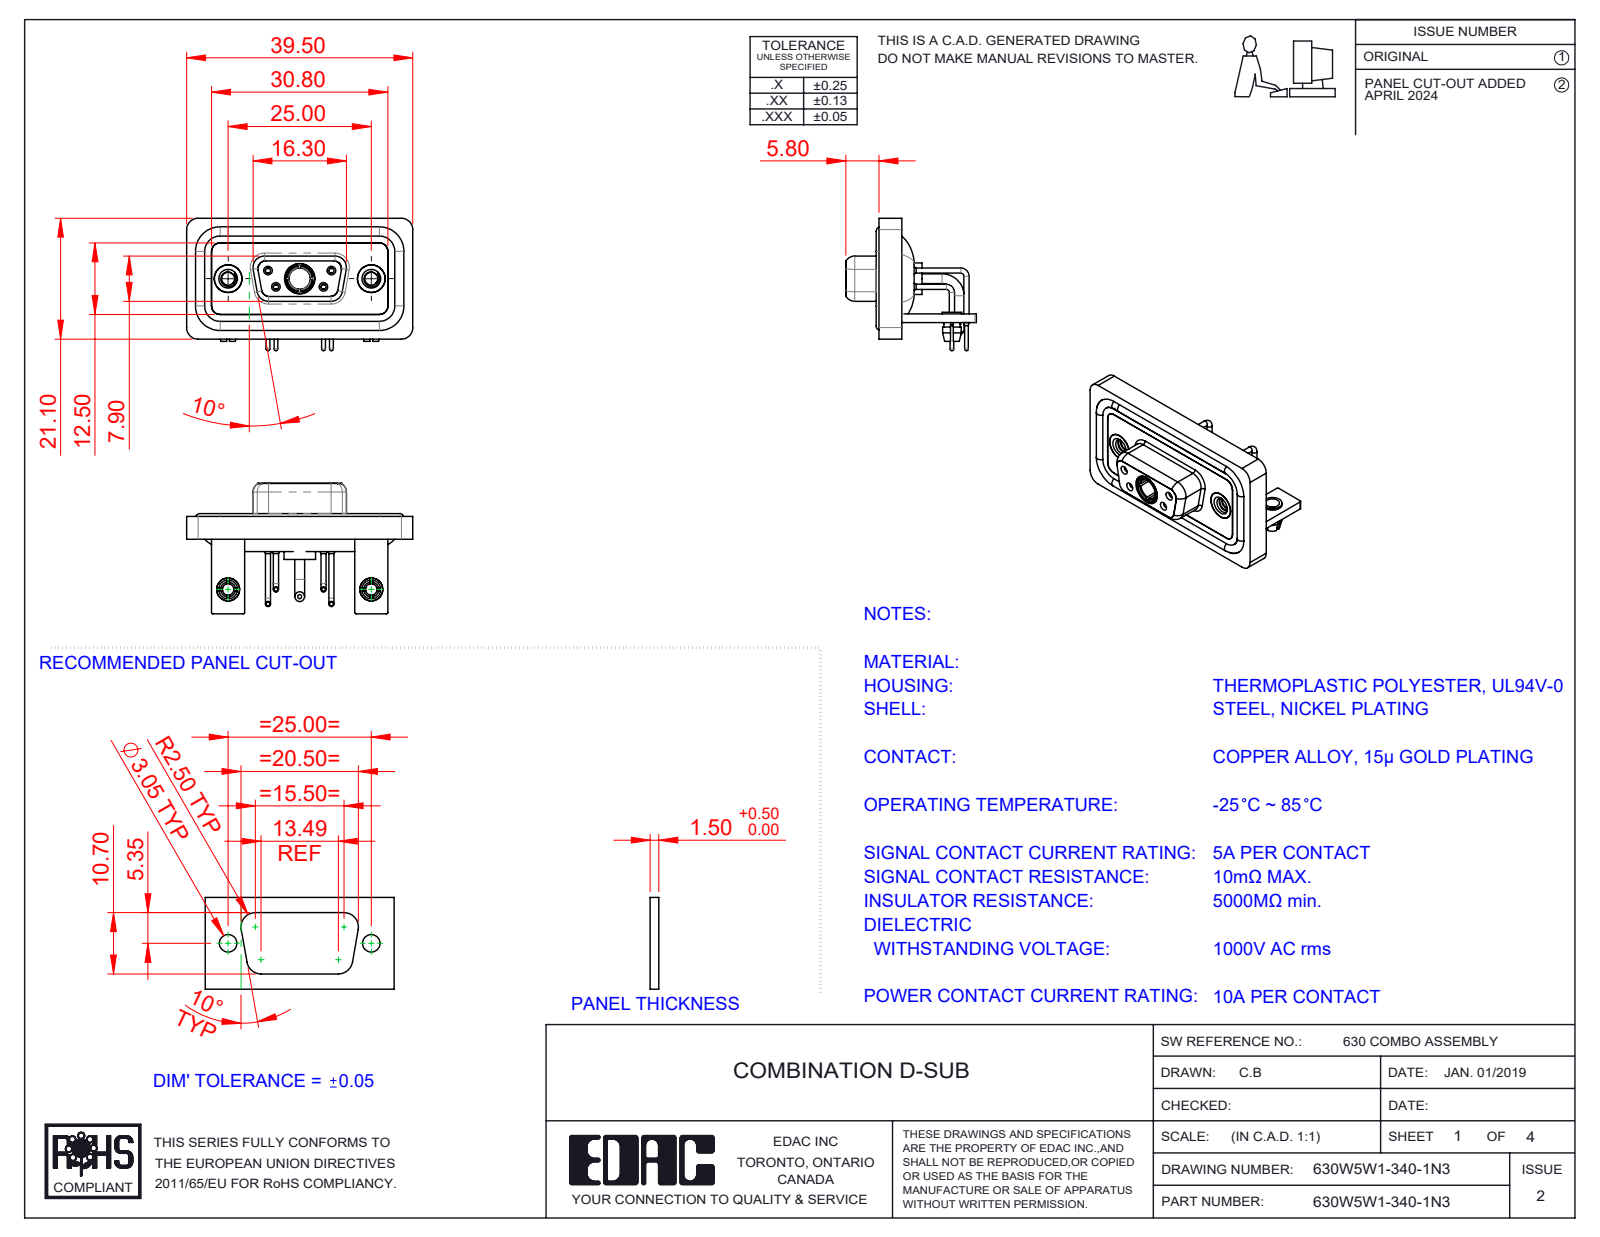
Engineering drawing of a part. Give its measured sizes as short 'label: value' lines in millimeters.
name: 630Combo Shell Front_09 Contacts; Power Socket_10A RA; 630Combo Housing_5W1; 630Combo Shell Rear_09 Contacts (+7 more)
written by: SolidWorks 2023 (CONFIG_CONTROL_DESIGN)
unit: mm
bodies: 17 solids, 816 faces (262 planar, 361 cylindrical, 193 other)
size: 39.5 × 23.12 × 22.8
volume: 5 174 mm³; area: 8 738 mm²
holes: 6× ⌀2, 4× ⌀0.9, 4× ⌀1.1, 4× ⌀1.5, 3× ⌀4.85, 2× ⌀1.6, 2× ⌀1.7, 2× ⌀2.26, 2× ⌀2.5, 2× ⌀3.2, 2× ⌀4, 2× ⌀4.05
bosses: 6× ⌀1.6, 4× ⌀0.9, 4× ⌀0.65, 2× ⌀4.95, 2× ⌀4.8, 2× ⌀4, 2× ⌀3.4, 2× ⌀3.3
rounds: 19× R2, 18× R1.5, 16× R0.25, 8× R1.35, 8× R1.6, 5× R0.5, 4× R0.6, 4× R0.65
face distances: 0.4, 2.9, 1.5, 1.8, 1.1, 3.7, 1.6, 0.8, 2.5, 3.1
hole spacings: 3.16, 5.72, 7.1, 12.5, 18.1, 25, 4.39, 4.4
